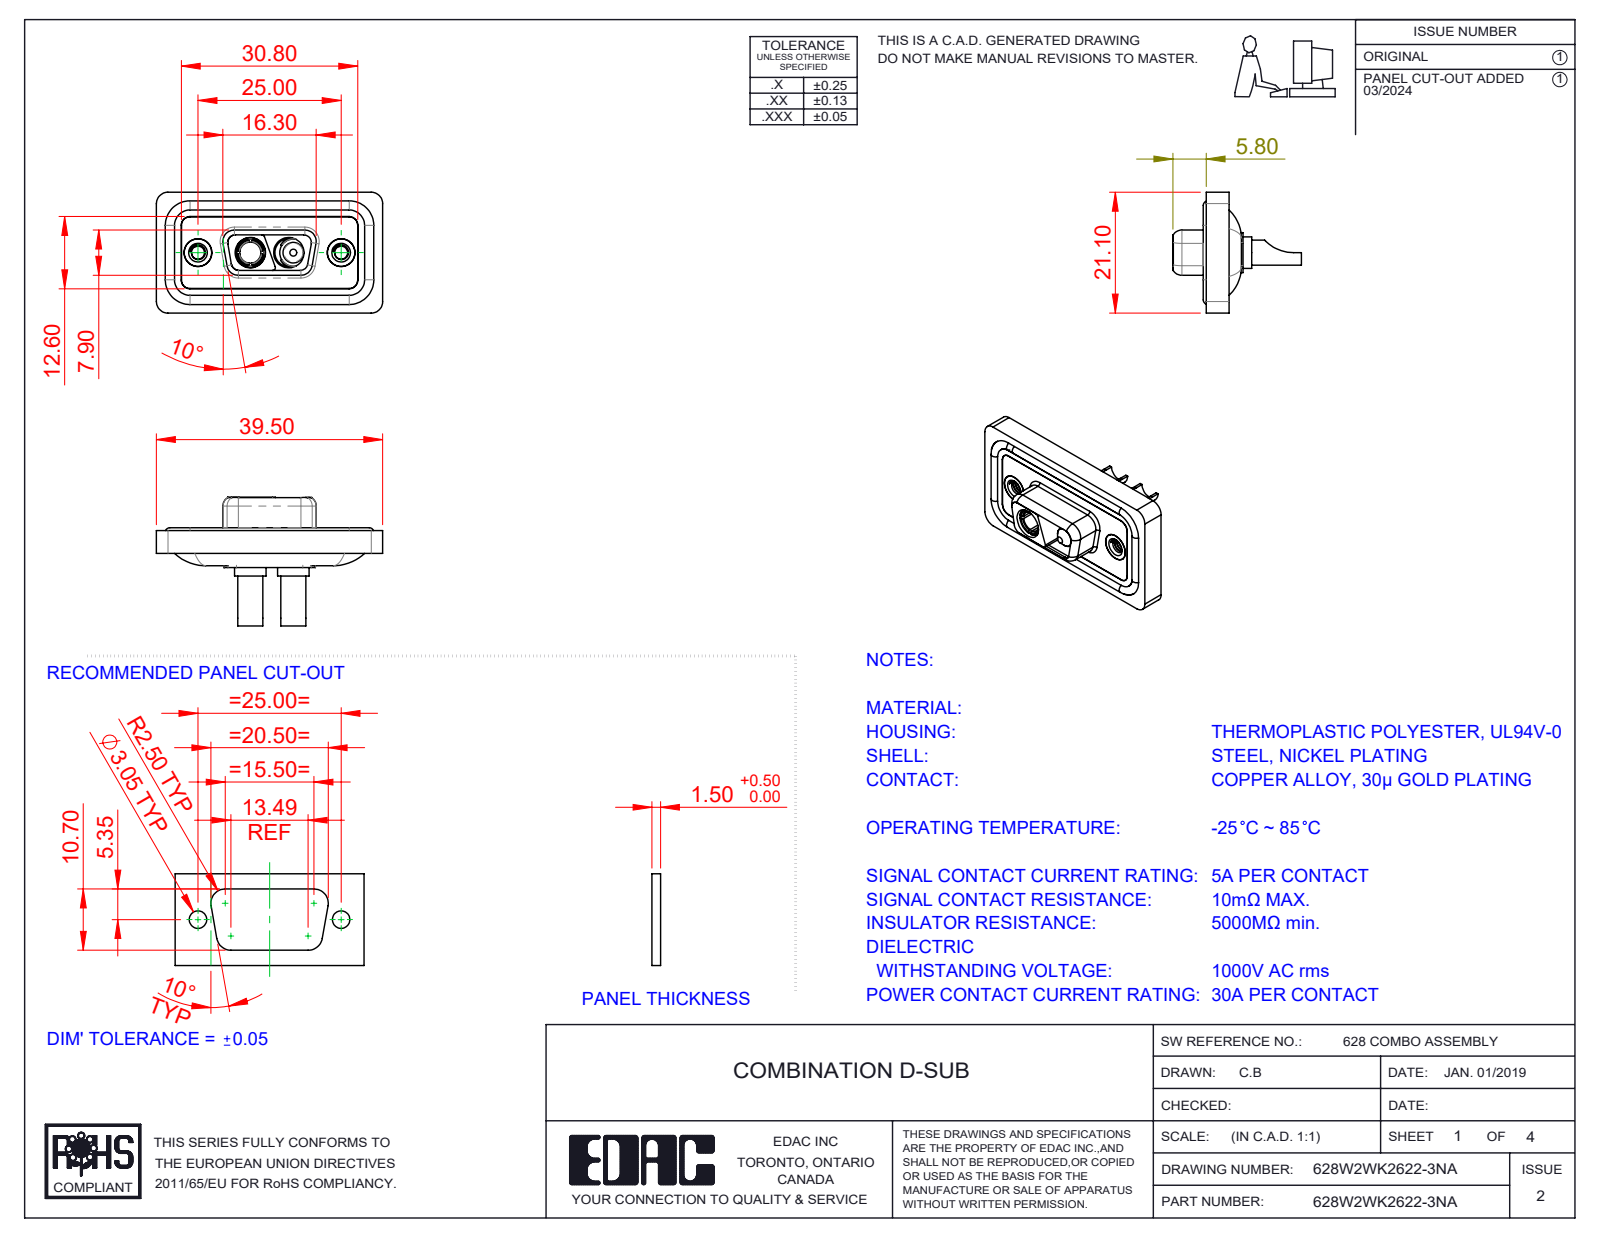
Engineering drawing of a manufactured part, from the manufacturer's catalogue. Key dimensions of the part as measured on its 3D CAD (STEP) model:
Part name (STEP PRODUCT): 628W2WK2622-3NA; 628Combo Housing_2WK2; 628Combo Shell Rear_09 Contacts; 628Combo Threaded Rivet_A (+4 more)
STEP written by: SolidWorks 2023 (CONFIG_CONTROL_DESIGN)
Units: millimetres
Bodies: 11 solids, 510 faces (150 planar, 239 cylindrical, 121 other)
Overall size (bounding box): 39.5 × 22.45 × 21.1
Volume: 4 653 mm³ · Surface area: 7 556 mm²
Round holes (diameter × count): ⌀4.85 ×4, ⌀2.26 ×2, ⌀3.5 ×2, ⌀4 ×2, ⌀4.05 ×2, ⌀5 ×2, ⌀5.3 ×2, ⌀3.7 ×1
Round bosses / shafts (diameter × count): ⌀1.6 ×4, ⌀5.5 ×2, ⌀5.2 ×2, ⌀4.95 ×2, ⌀4.8 ×2, ⌀4.75 ×2, ⌀4.4 ×2, ⌀3.75 ×2
Partial cylindrical surfaces — rounded edges, fillets, slot ends (radius × count): R1.5 ×22, R2 ×18, R1.35 ×8, R1.6 ×8, R0.5 ×6, R0.25 ×4, R0.6 ×4, R0.65 ×4
Main face-to-face distances: 0.4, 1.1, 2.9, 1.6, 0.5, 1.8, 5.65, 5.35, 3.1, 0.7
Hole centre spacings: 9.14, 15.86, 6.72, 25
